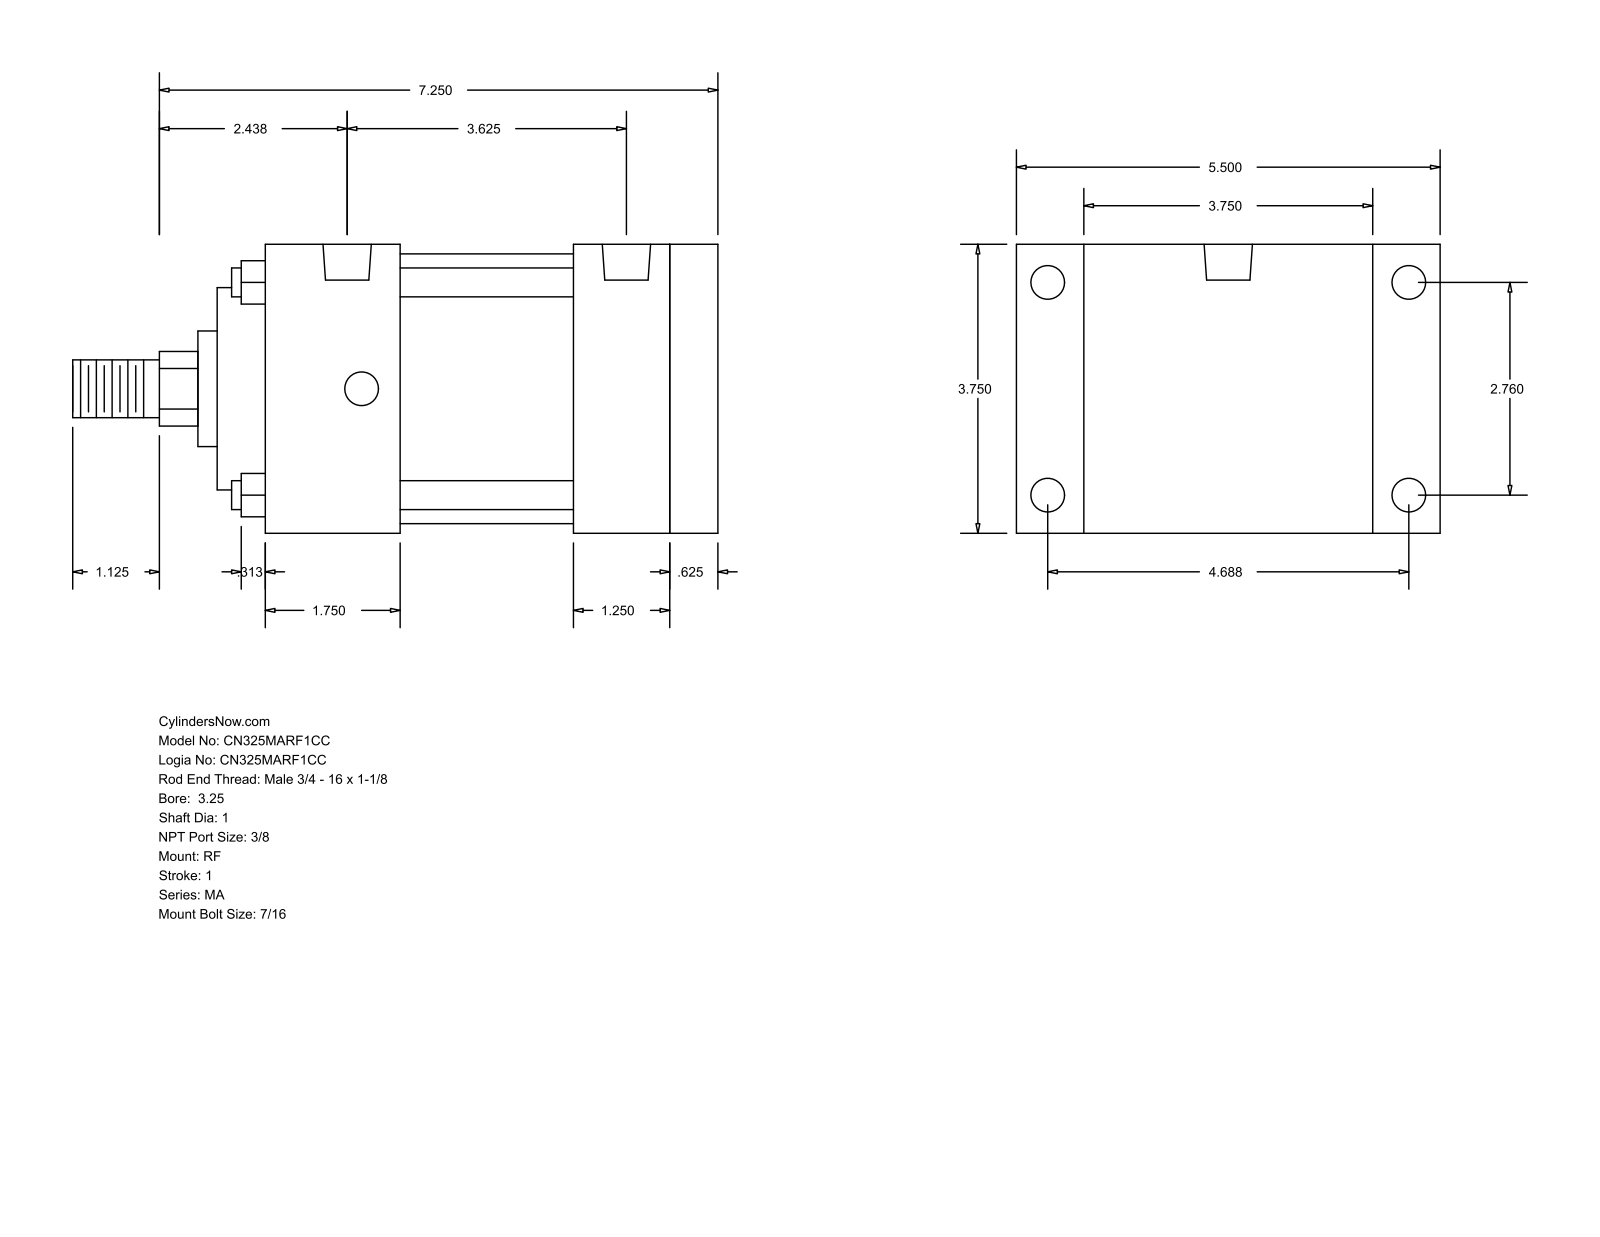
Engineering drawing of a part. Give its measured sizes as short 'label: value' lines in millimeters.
name: MA_RF__0325_1
written by: GSSL Pune (CONFIG_CONTROL_DESIGN)
unit: mm
bodies: 0 solids, 94 faces (65 planar, 29 cylindrical, 0 other)
size: 212.72 × 139.7 × 95.25
holes: 8× ⌀11.11, 2× ⌀15.93
bosses: 4× ⌀9.53, 1× ⌀88.9, 1× ⌀66.67, 1× ⌀38.1, 1× ⌀25.4, 1× ⌀19.05
rounds: 1× R12.29
face distances: 95.24, 149.23, 15.87, 133.36, 22.23, 117.47, 47.62, 165.1, 101.61, 31.75
hole spacings: 70.1, 82.55, 119.06, 138.16, 4.76, 4.77, 87.31, 87.32
